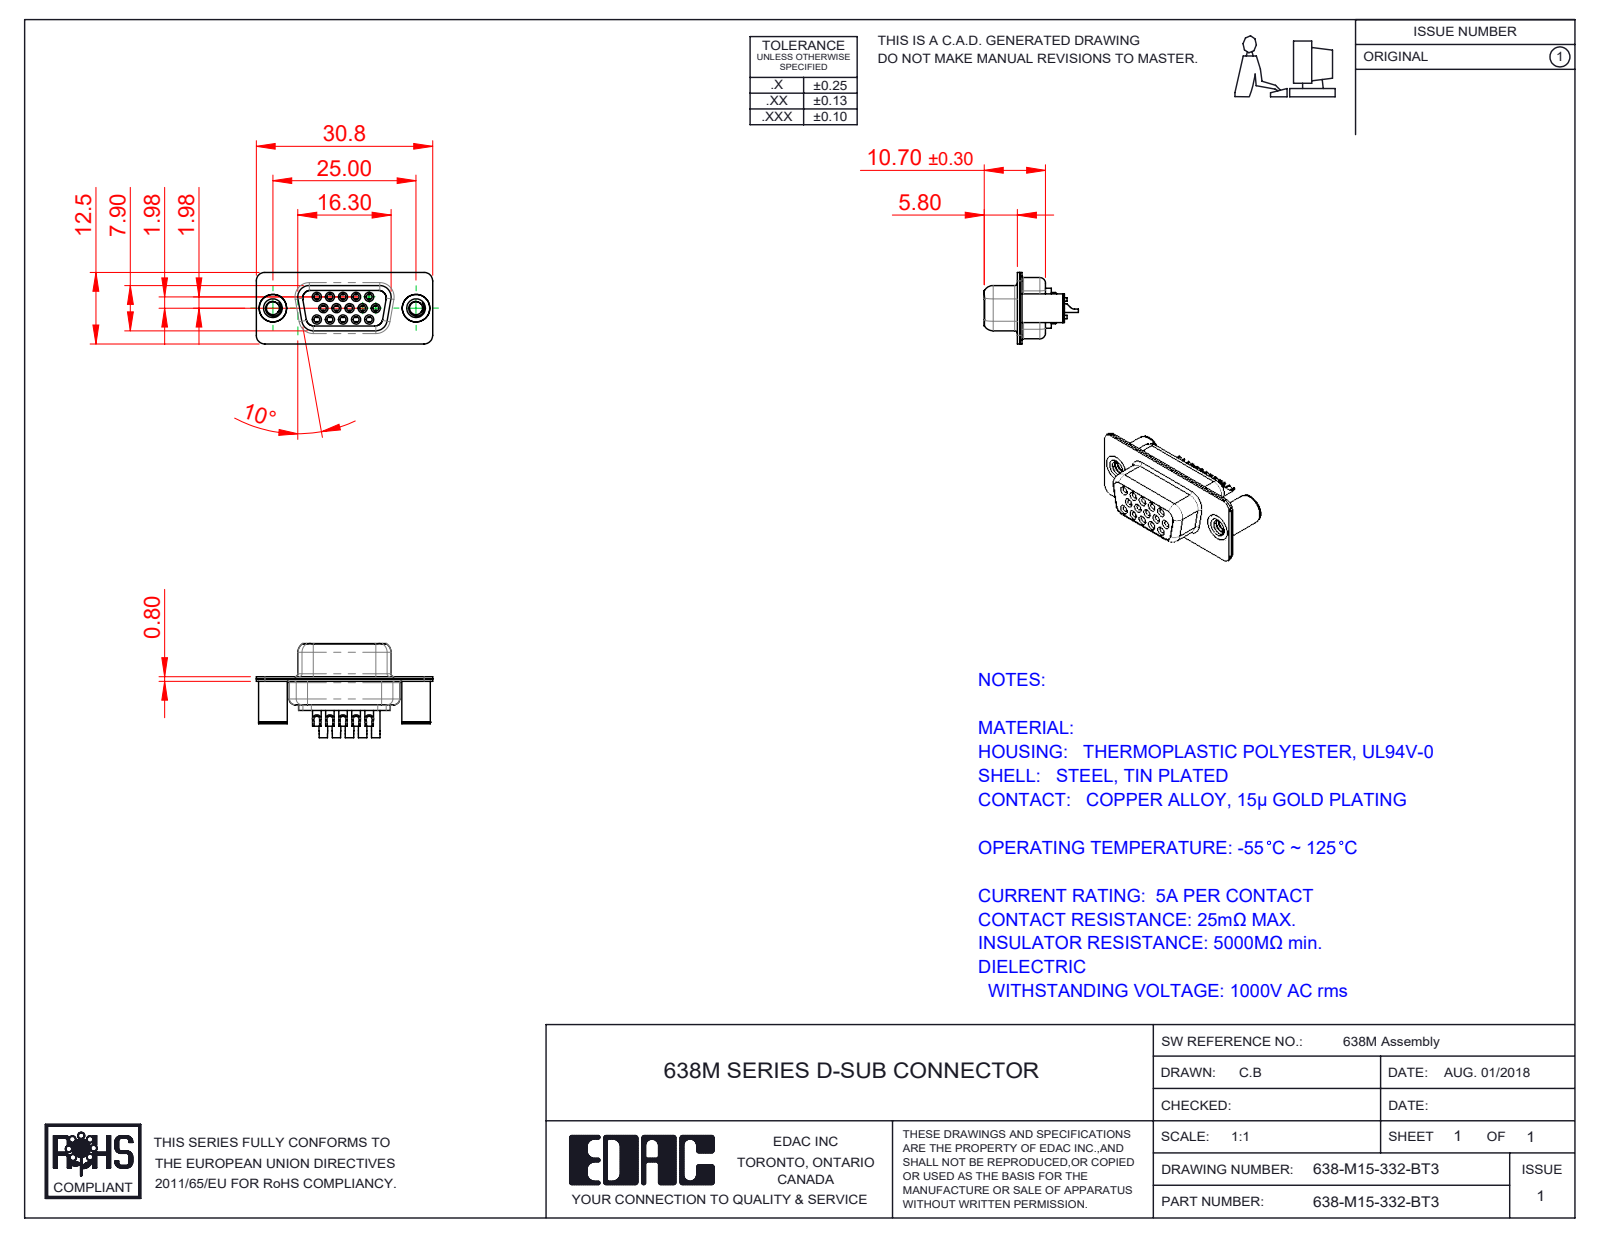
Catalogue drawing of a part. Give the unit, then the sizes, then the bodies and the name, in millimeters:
Units: millimetres
Overall size (bounding box): 30.8 × 16.45 × 12.5
Round holes (diameter × count): ⌀1 ×16, ⌀1.1 ×15, ⌀1.7 ×15, ⌀1.8 ×15, ⌀2 ×15, ⌀2.26 ×2, ⌀3.26 ×2, ⌀4 ×2, ⌀4.8 ×2
Round bosses / shafts (diameter × count): ⌀2.2 ×15, ⌀1.6 ×15, ⌀1.5 ×15, ⌀5 ×2, ⌀4.9 ×2
Partial cylindrical surfaces — rounded edges, fillets, slot ends (radius × count): R1.5 ×16, R2 ×12, R1.35 ×8, R1.6 ×8, R1 ×7, R0.25 ×4, R0.5 ×4, R0.6 ×4
Main face-to-face distances: 0.4, 1.4, 0.45, 8.45, 0.8, 8.9, 1, 1.8, 6.2, 7.05
Hole centre spacings: 2.28, 3.96, 2.29, 4.57, 6.05, 6.04, 6.86, 7.92
Volume: 1 782 mm³ · Surface area: 5 691 mm²
Bodies: 20 solids, 1138 faces (322 planar, 476 cylindrical, 340 other)
Part name (STEP PRODUCT): 638-M15-332-BT3; 638M Contact Row 2_32; 638M Shell Front_15 Contacts; 638M Contact Row 3_32 (+4 more)
STEP written by: SolidWorks 2020 (CONFIG_CONTROL_DESIGN)
